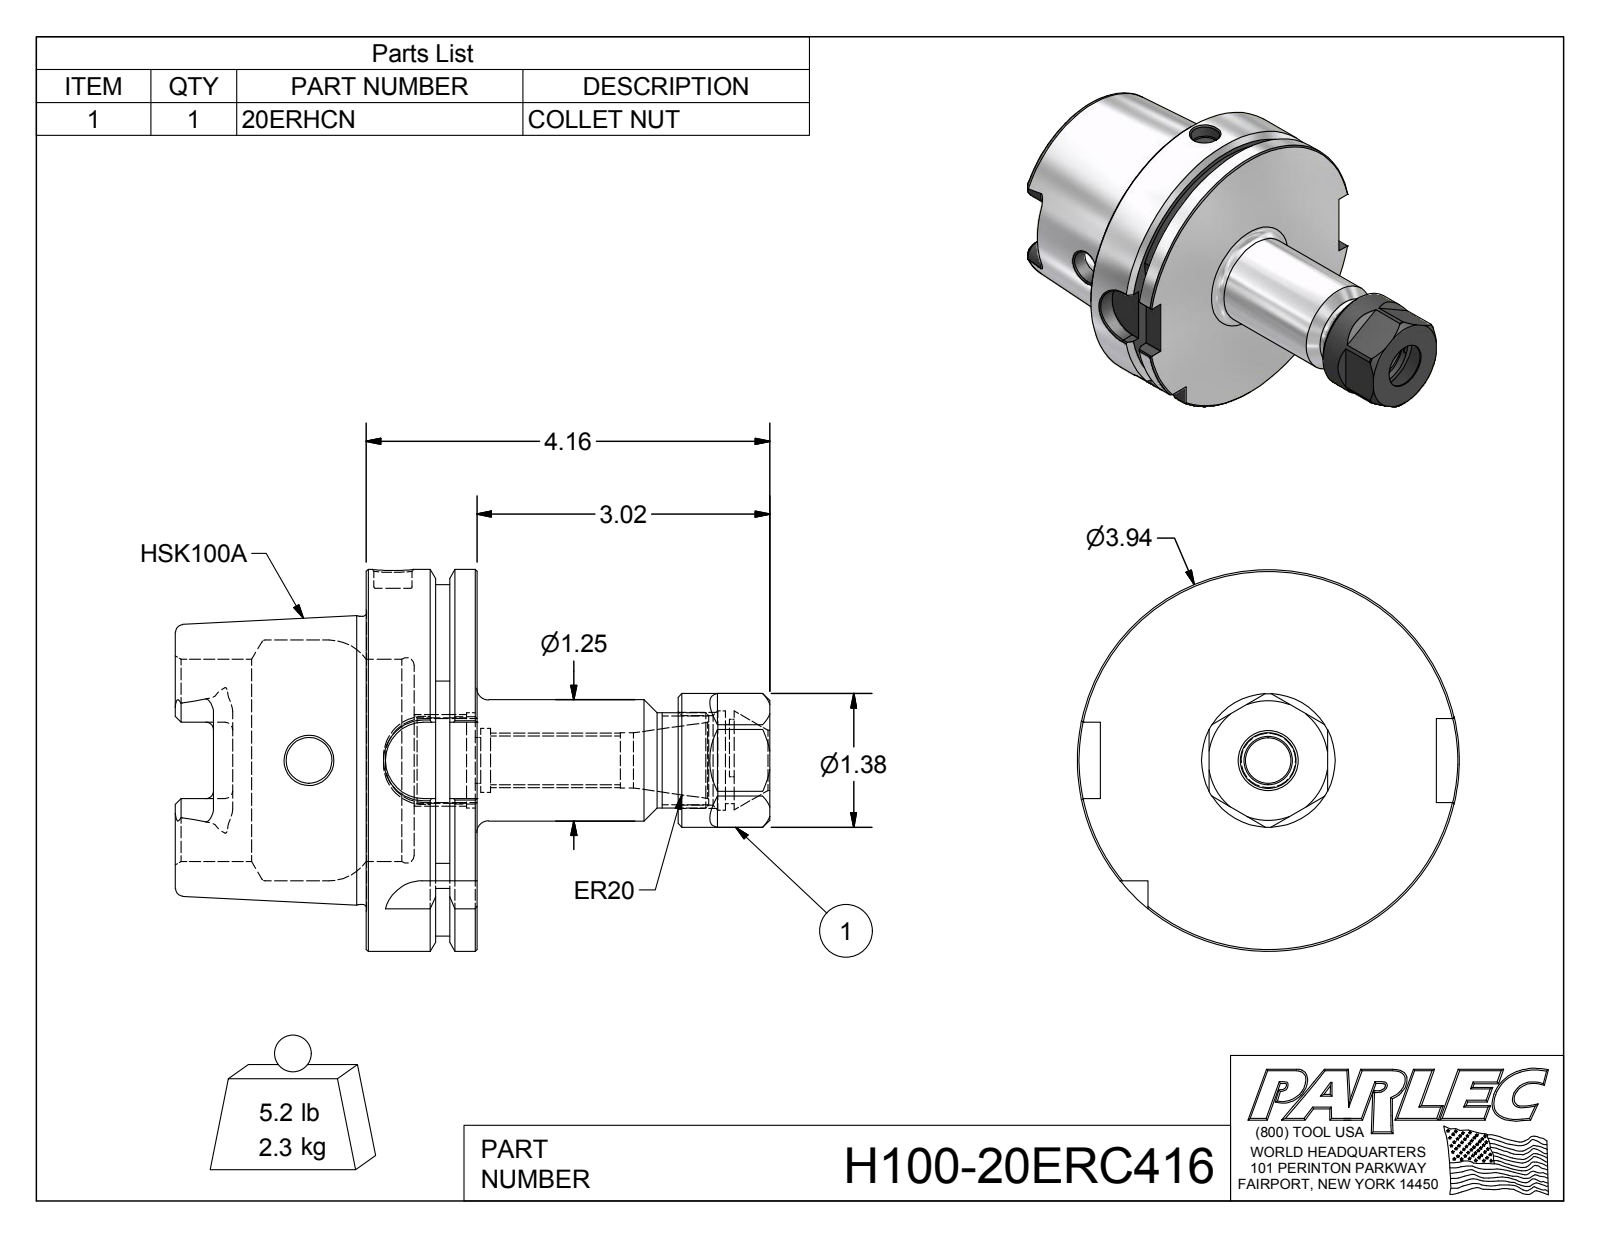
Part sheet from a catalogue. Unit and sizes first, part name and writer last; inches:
Units: inches
Overall size (bounding box): 6.129 × 3.937 × 3.937
Round holes (diameter × count): ⌀0.472 ×2, ⌀0.394 ×1, ⌀0.472 ×1, ⌀0.502 ×1, ⌀0.57 ×1, ⌀0.62 ×1, ⌀0.663 ×1, ⌀0.82 ×1, ⌀0.881 ×1, ⌀0.925 ×1, ⌀0.985 ×1, ⌀1.024 ×1
Round bosses / shafts (diameter × count): ⌀3.937 ×1, ⌀2.967 ×1, ⌀1.378 ×1, ⌀1.25 ×1, ⌀0.984 ×1
Partial cylindrical surfaces — rounded edges, fillets, slot ends (radius × count): R0.079 ×6, R0.192 ×4, R0.394 ×4, R0.423 ×1, R1.811 ×1
Main face-to-face distances: 1.142, 0.492, 0.65, 1.969, 2.461, 3.11, 1.122, 1.22, 0.63, 3.018
Hole centre spacings: 0.037
Volume: 18.22 in³ · Surface area: 99.07 in²
Bodies: 2 solids, 171 faces (63 planar, 43 cylindrical, 65 other)
Part name (STEP PRODUCT): H100-20ERC416; H100-20ER4-1; 20ERHCN
STEP written by: Autodesk Inventor 2012 (AUTOMOTIVE_DESIGN)
